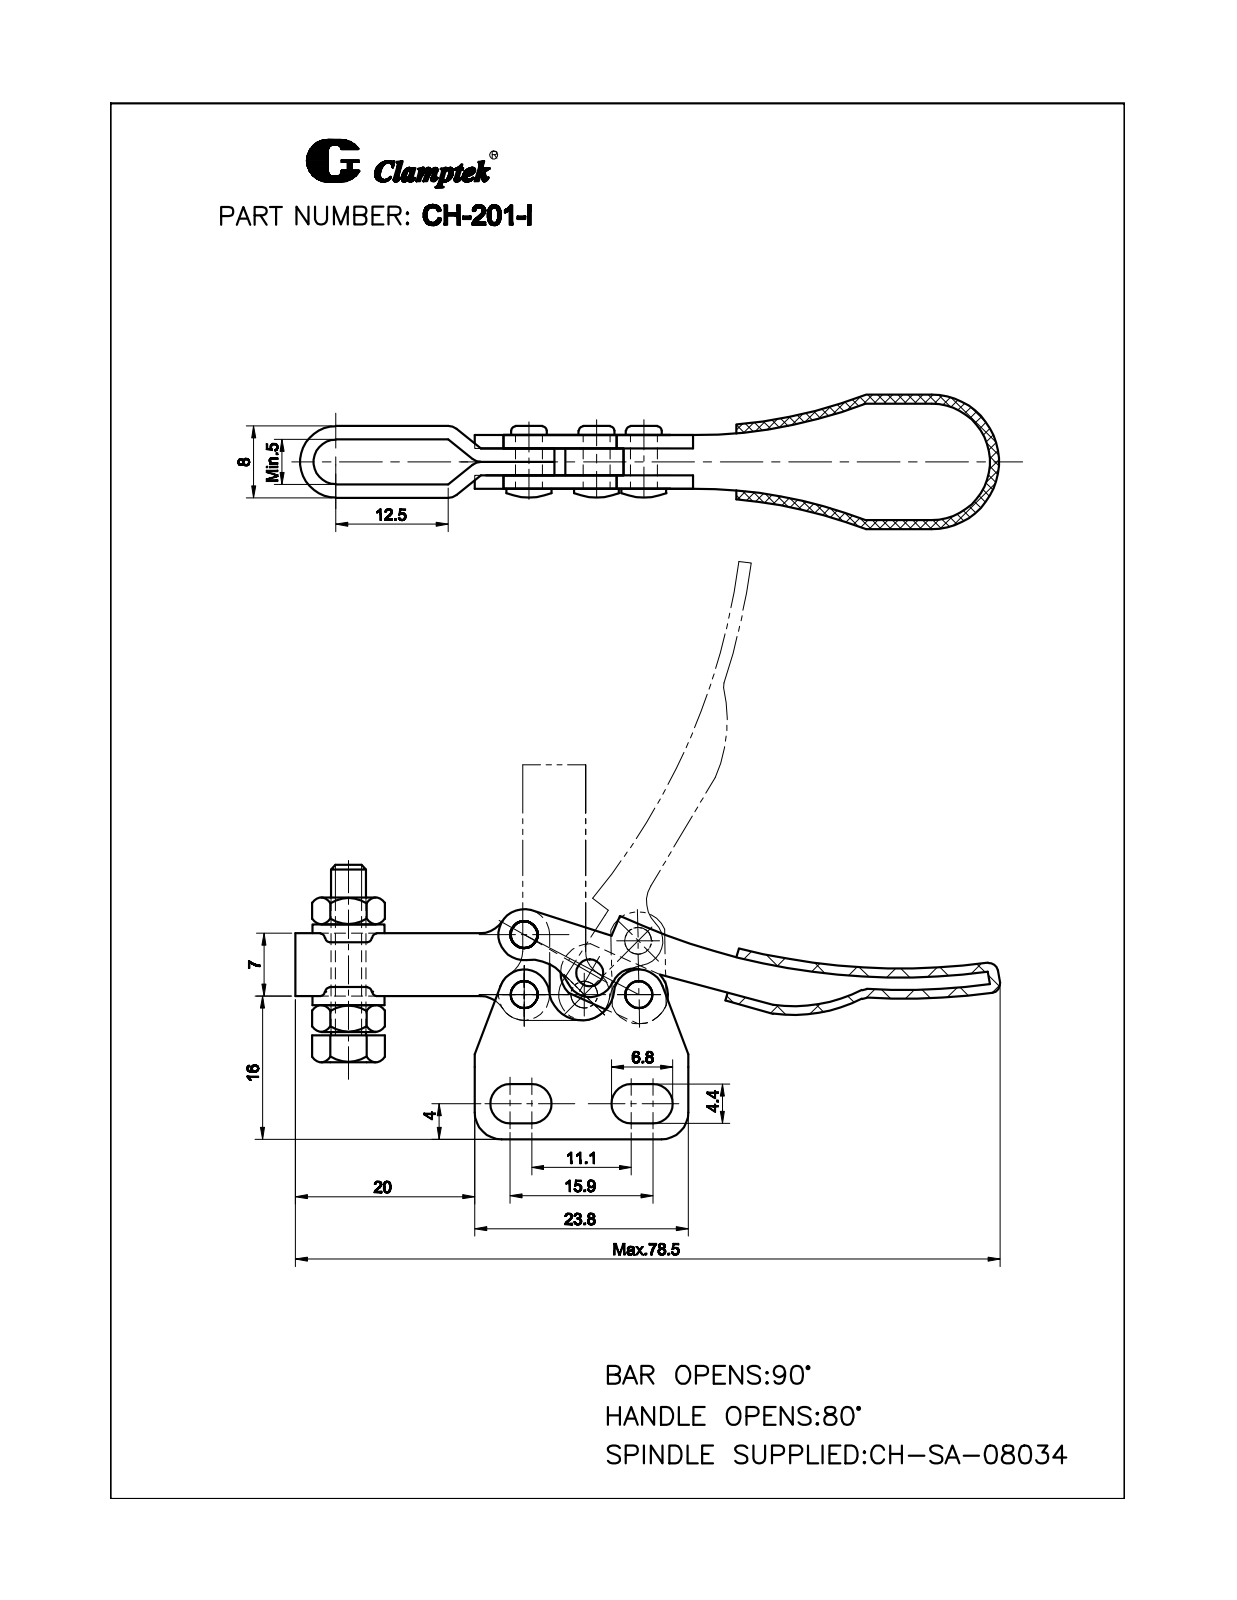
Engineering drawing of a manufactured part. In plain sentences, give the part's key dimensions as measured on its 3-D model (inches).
The part is named "CH-201-03 HANDLE; CH-201-A-04; CH-SA-042007 SPINDLE SUPPLIED; CH-FW-080 (+7 more)". Its 3-D file was written by "SolidWorks 2010 (CONFIG_CONTROL_DESIGN)". It is 17 solids with 748 faces: 273 planar, 218 cylindrical and 257 other. Overall it measures 3.1 by 1.138 by 0.591 inches. Its volume is 0.277 cubic inches and its surface area 13.31 square inches. Round holes: 4 of diameter 0.094, 4 of diameter 0.118, 1 of diameter 0.023, 1 of diameter 0.126, 1 of diameter 0.169. Round bosses or shafts: 1 of diameter 0.157, 1 of diameter 0.02. Partial cylindrical surfaces (rounded edges, fillets, slot ends): 9 of radius 0.039, 4 of radius 0.059, 4 of radius 0.087, 4 of radius 0.112, 2 of radius 0.098, 2 of radius 0.11, 2 of radius 0.118, 2 of radius 0.128. The main face-to-face distances are 0.059, 0.118, 0.177, 0.039, 0.236, 0.276, 0.157, 0.098, 0.217, 0.315. The hole center spacings are 0.18, 0.236, 0.264, 0.314, 0.335, 0.345, 0.433, 0.453.
